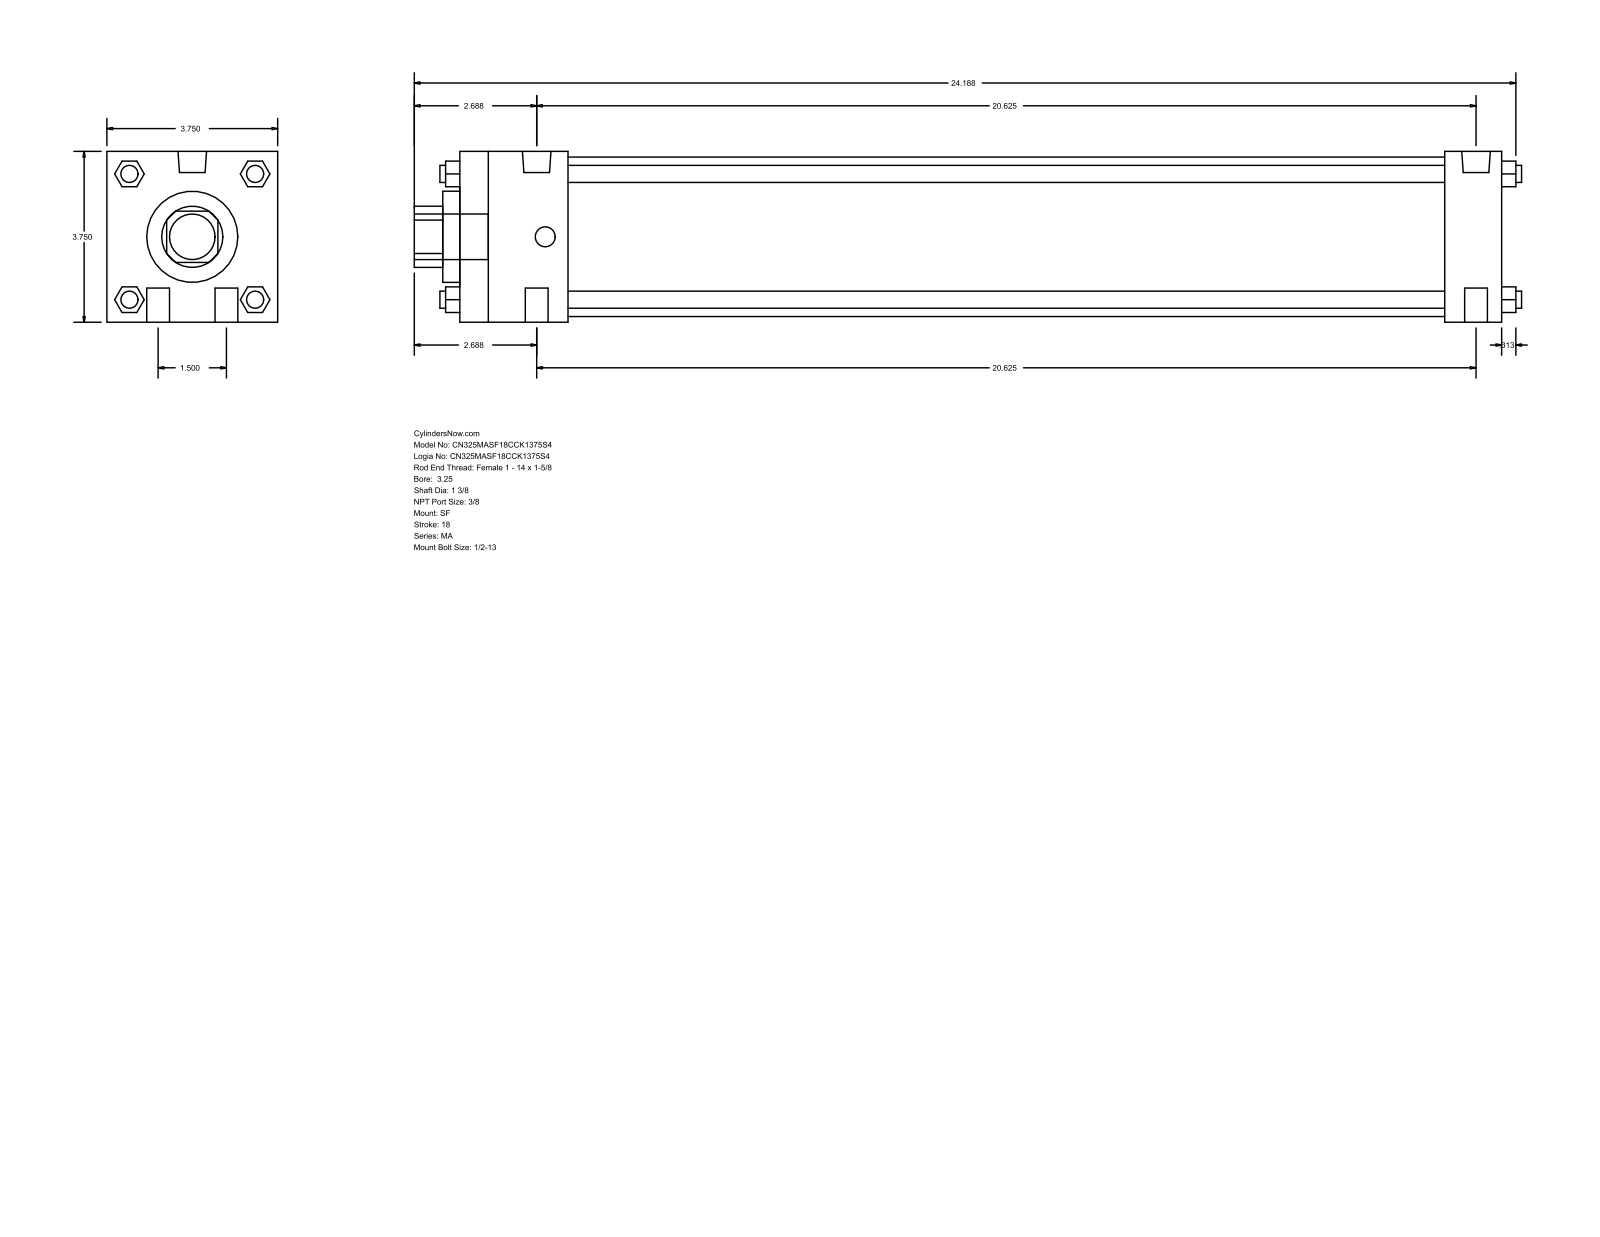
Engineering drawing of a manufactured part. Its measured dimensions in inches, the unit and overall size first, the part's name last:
Units: inches
Overall size (bounding box): 24.313 × 3.75 × 3.75
Round holes (diameter × count): ⌀1.375 ×1, ⌀2 ×1, ⌀3.5 ×1
Round bosses / shafts (diameter × count): ⌀0.5 ×4, ⌀0.375 ×4, ⌀0.627 ×2, ⌀0.437 ×2, ⌀1 ×1
Partial cylindrical surfaces — rounded edges, fillets, slot ends (radius × count): R0.672 ×1
Main face-to-face distances: 3.75, 22.875, 21.625, 1.25, 2.375, 19.25, 20.5, 0.375, 2.75, 22
Bodies: 0 solids, 124 faces (94 planar, 30 cylindrical, 0 other)
Part name (STEP PRODUCT): MA_SF__0325_1.375
STEP written by: GSSL Pune (CONFIG_CONTROL_DESIGN)
